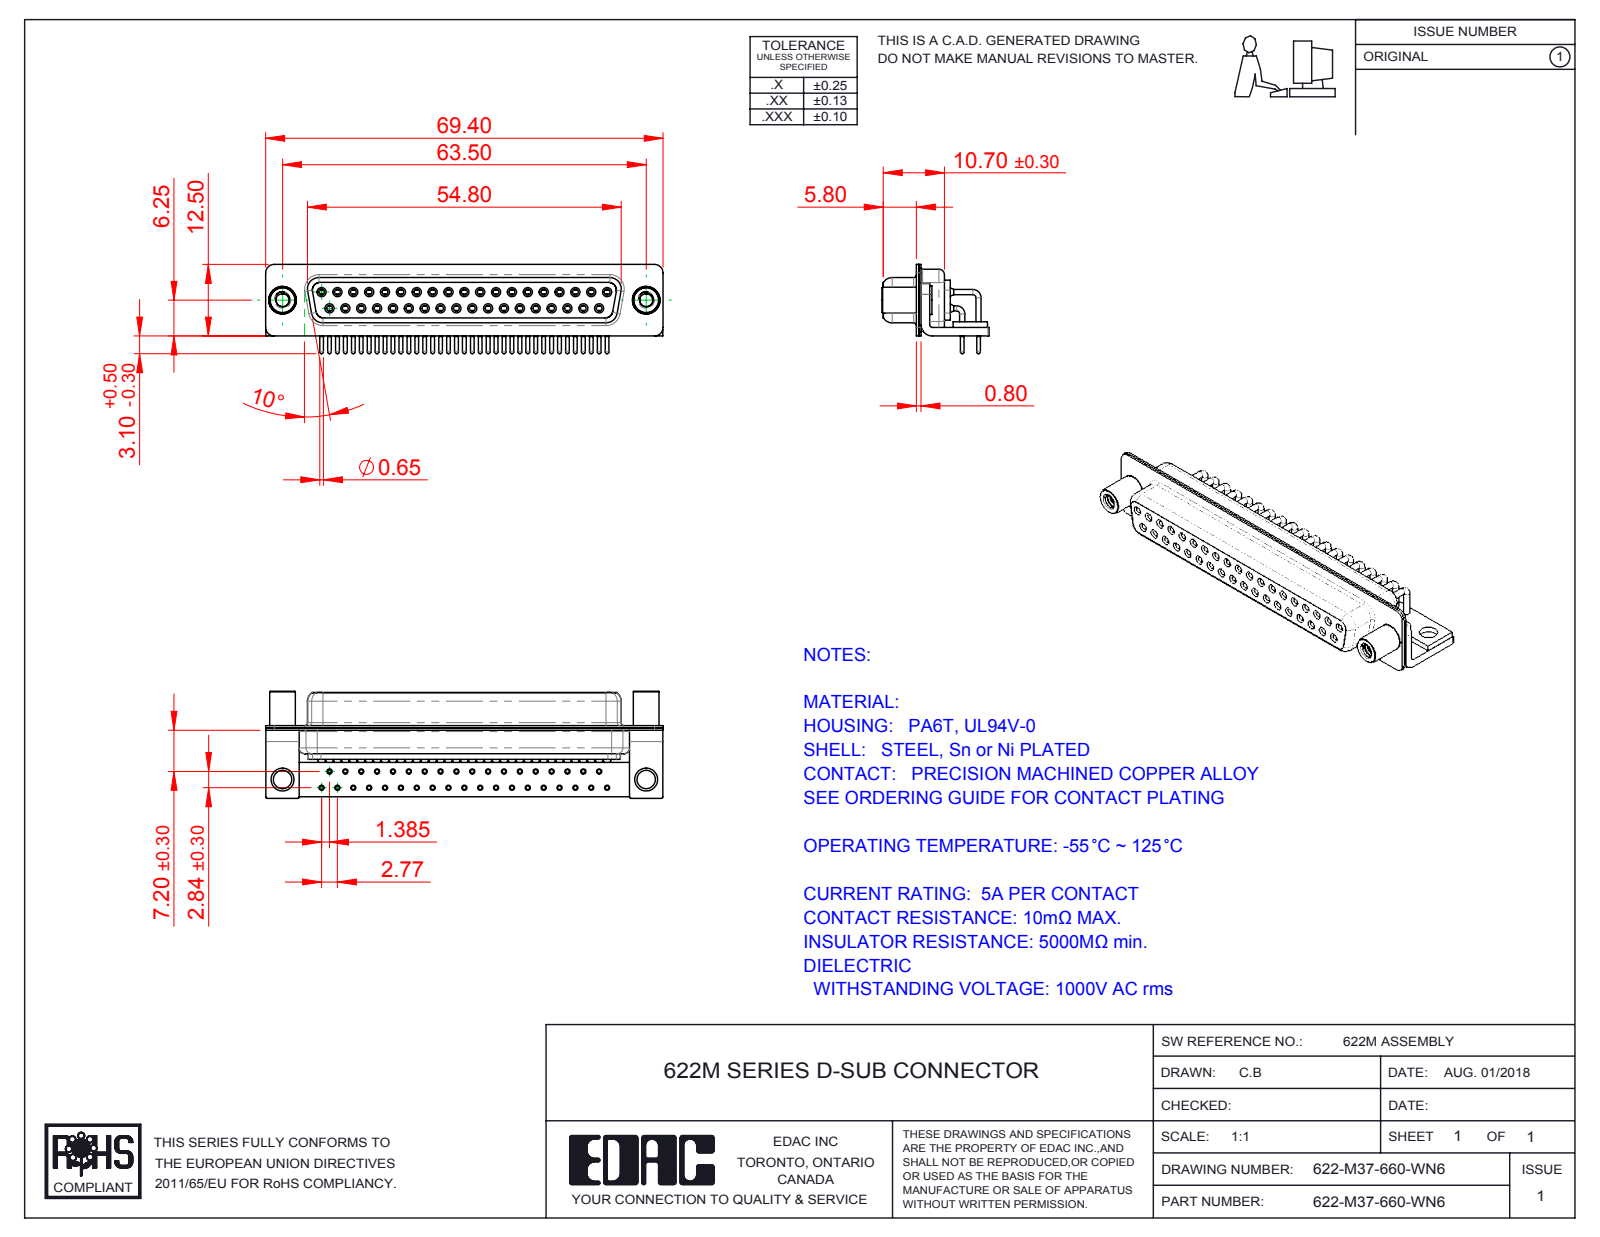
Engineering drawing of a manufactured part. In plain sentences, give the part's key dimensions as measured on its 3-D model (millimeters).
The part is named "622M Shell Front_37 Contacts; 622M 4-40 Threaded Standoff; 622M Shell Rear_37 Contacts; 622M Contact Row 2 (+5 more)". Its 3-D file was written by "SolidWorks 2016 (CONFIG_CONTROL_DESIGN)". It is 45 solids with 2414 faces: 650 planar, 1126 cylindrical and 638 other. Overall it measures 69.4 by 18.7 by 15.6 millimeters. Its volume is 6 145 cubic millimeters and its surface area 15 051 square millimeters. Round holes: 37 of diameter 0.9, 37 of diameter 1, 37 of diameter 1.1, 37 of diameter 1.7, 37 of diameter 1.8, 37 of diameter 2, 2 of diameter 2.26, 2 of diameter 3.2, 2 of diameter 4, 2 of diameter 4.8. Round bosses or shafts: 54 of diameter 0.9, 37 of diameter 1.6, 37 of diameter 1.5, 37 of diameter 0.65, 2 of diameter 5, 2 of diameter 4.9, 2 of diameter 4.5. Partial cylindrical surfaces (rounded edges, fillets, slot ends): 16 of radius 0.25, 16 of radius 1.5, 13 of radius 2, 8 of radius 1.35, 8 of radius 1.6, 5 of radius 0.5, 4 of radius 0.6, 4 of radius 0.65. The main face-to-face distances are 0.4, 2.3, 1.9, 1.45, 8.95, 6.2, 0.85, 8.5, 0.45, 7.05. The hole center spacings are 2.77, 5.54, 3.16, 8.31, 11.08, 13.85, 16.62, 19.39.
